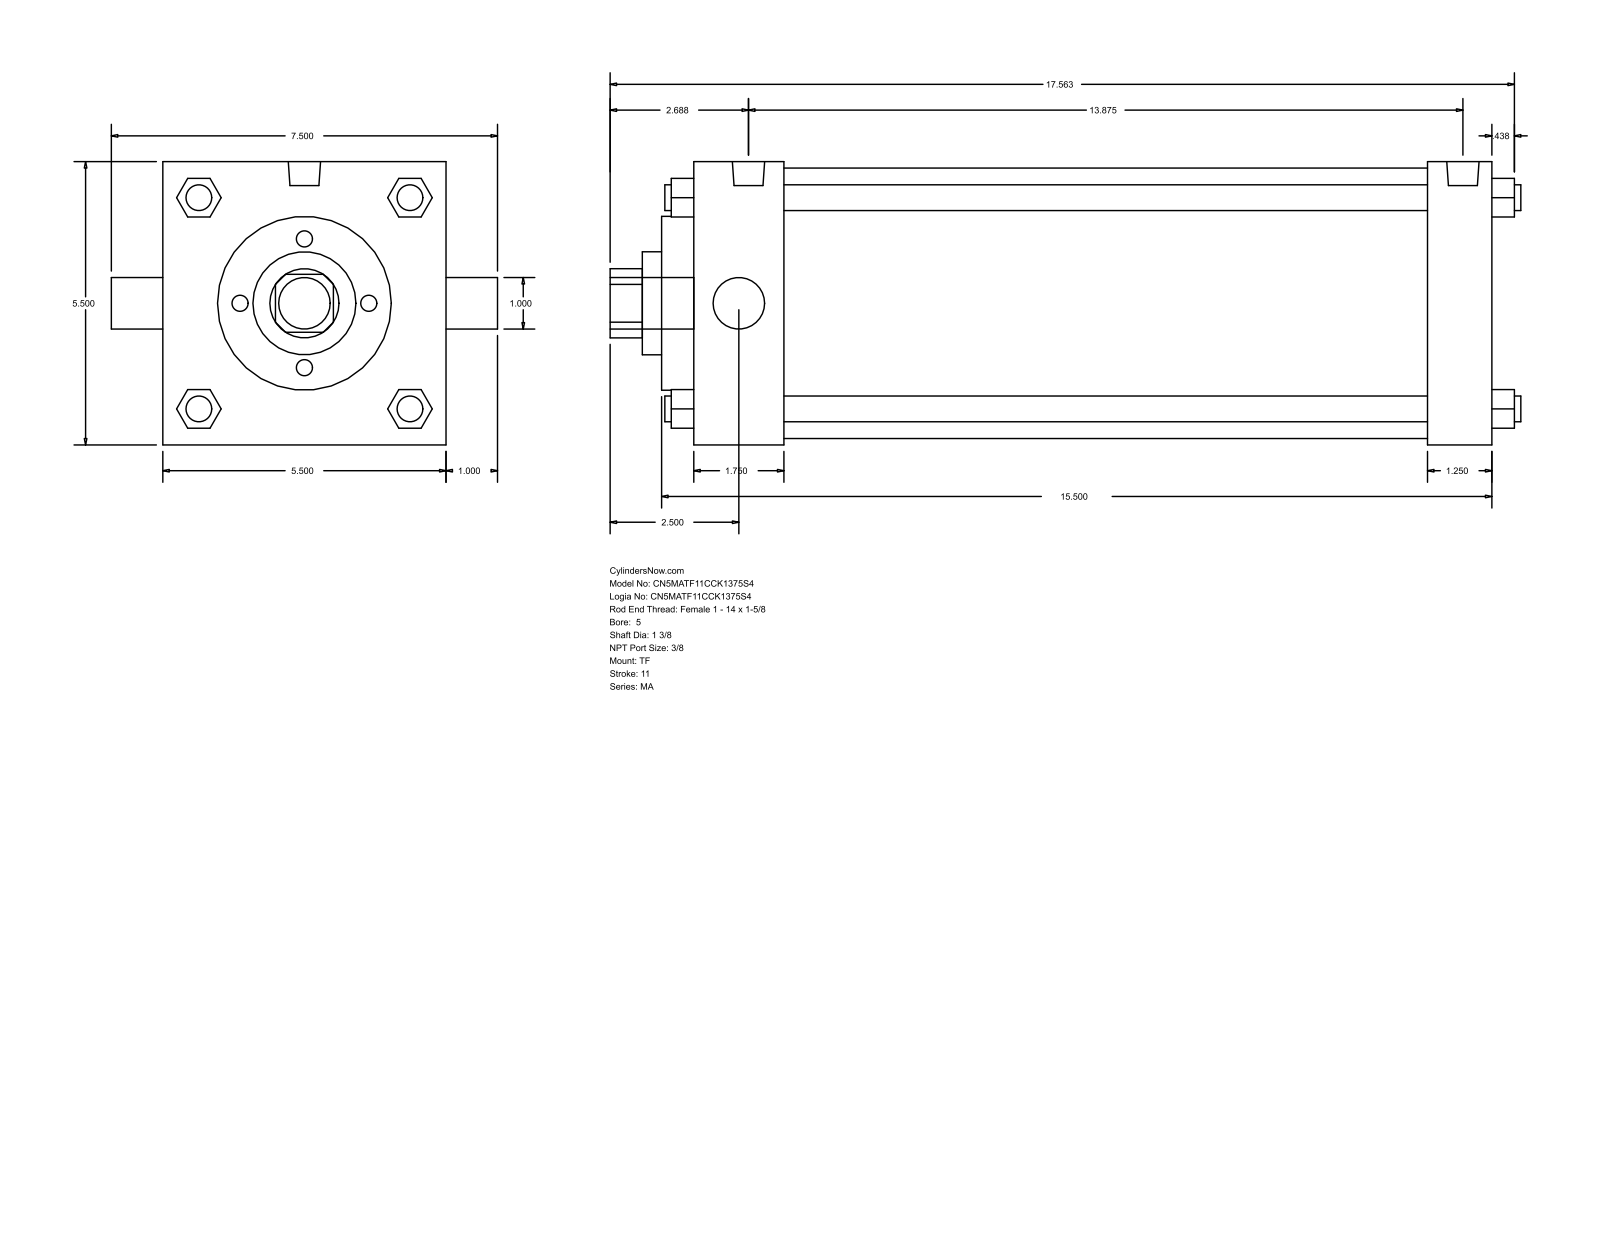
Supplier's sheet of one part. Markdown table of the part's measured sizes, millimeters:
| quantity | value |
| --- | --- |
| part name | MA_TF__0500_1.375 |
| STEP written by | GSSL Pune (CONFIG_CONTROL_DESIGN) |
| units | millimeters |
| bodies | 0 solids, 122 faces (93 planar, 29 cylindrical, 0 other) |
| overall size | 449.26 × 190.5 × 139.7 |
| round holes (diameter × count) | 25.4 × 1, 34.92 × 1, 50.8 × 1, 85.72 × 1, 133.35 × 1 |
| round bosses / shafts (diameter × count) | 12.7 × 4, 11.11 × 3, 15.93 × 2, 25.4 × 1 |
| partial cylindrical surfaces (radius × count) | 17.06 × 1 |
| main face-to-face distances | 139.7, 393.71, 361.96, 31.75, 44.45, 317.51, 349.26, 15.87, 60.32, 377.83 |
